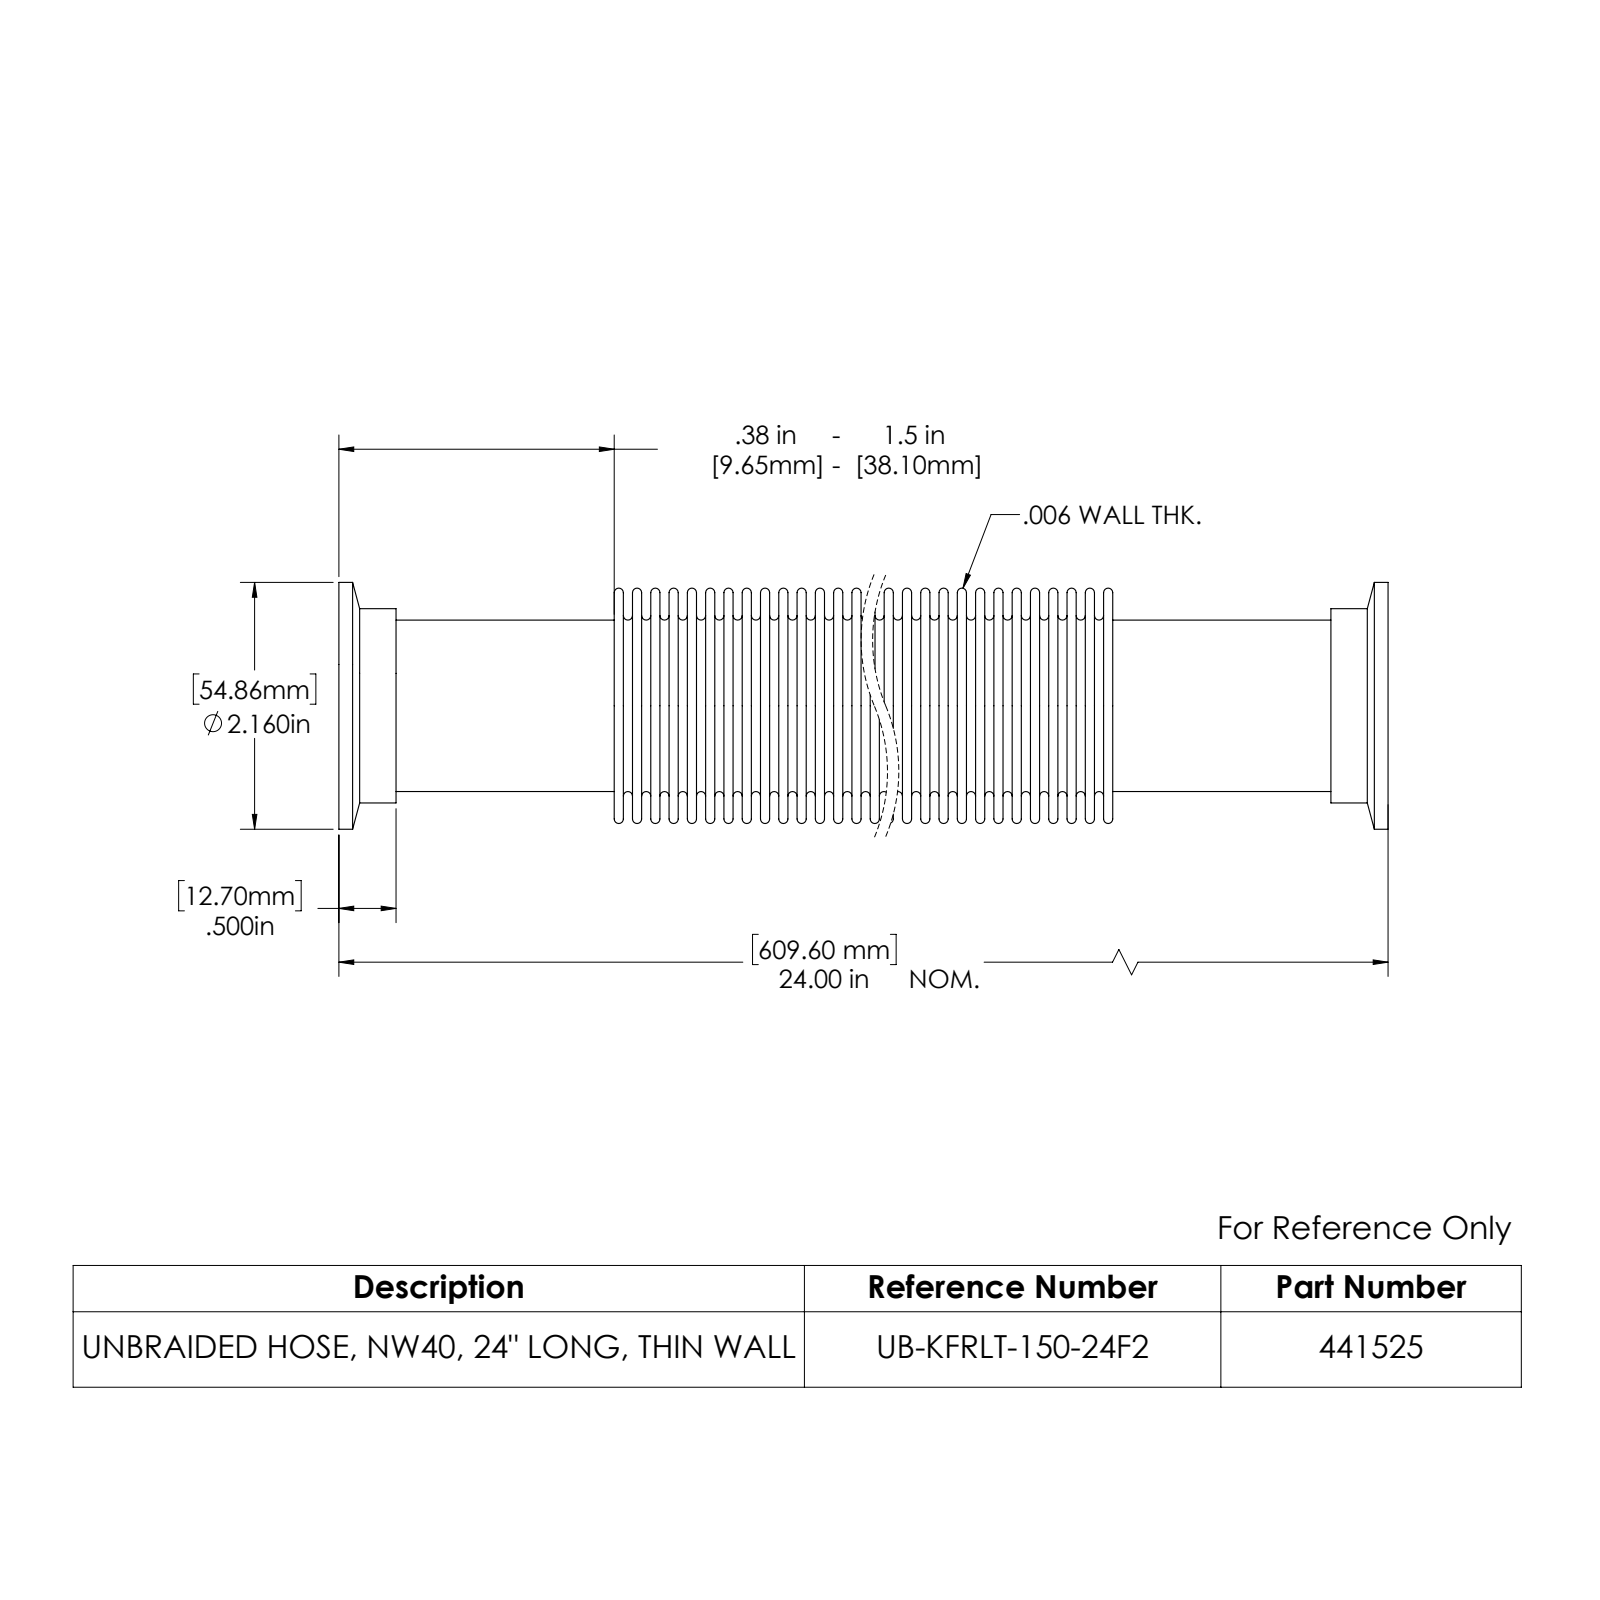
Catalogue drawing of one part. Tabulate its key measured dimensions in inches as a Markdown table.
| quantity | value |
| --- | --- |
| part name | 441525; 713003; 441541 |
| STEP written by | SolidWorks 2022 (CONFIG_CONTROL_DESIGN) |
| units | inches |
| bodies | 3 solids, 2002 faces (502 planar, 28 cylindrical, 1472 other) |
| overall size | 24.418 × 2.16 × 2.16 |
| volume | 5.551 in³ |
| surface area | 948.1 in² |
| round holes (diameter × count) | 1.375 × 1, 1.48 × 1, 1.51 × 1, 1.63 × 1 |
| round bosses / shafts (diameter × count) | 2.16 × 1, 1.7 × 1, 1.5 × 1 |
| main face-to-face distances | 0.32, 0.48, 0.8, 0.16, 0.64, 0.16, 1.12, 1.28, 0.96, 1.6 |
